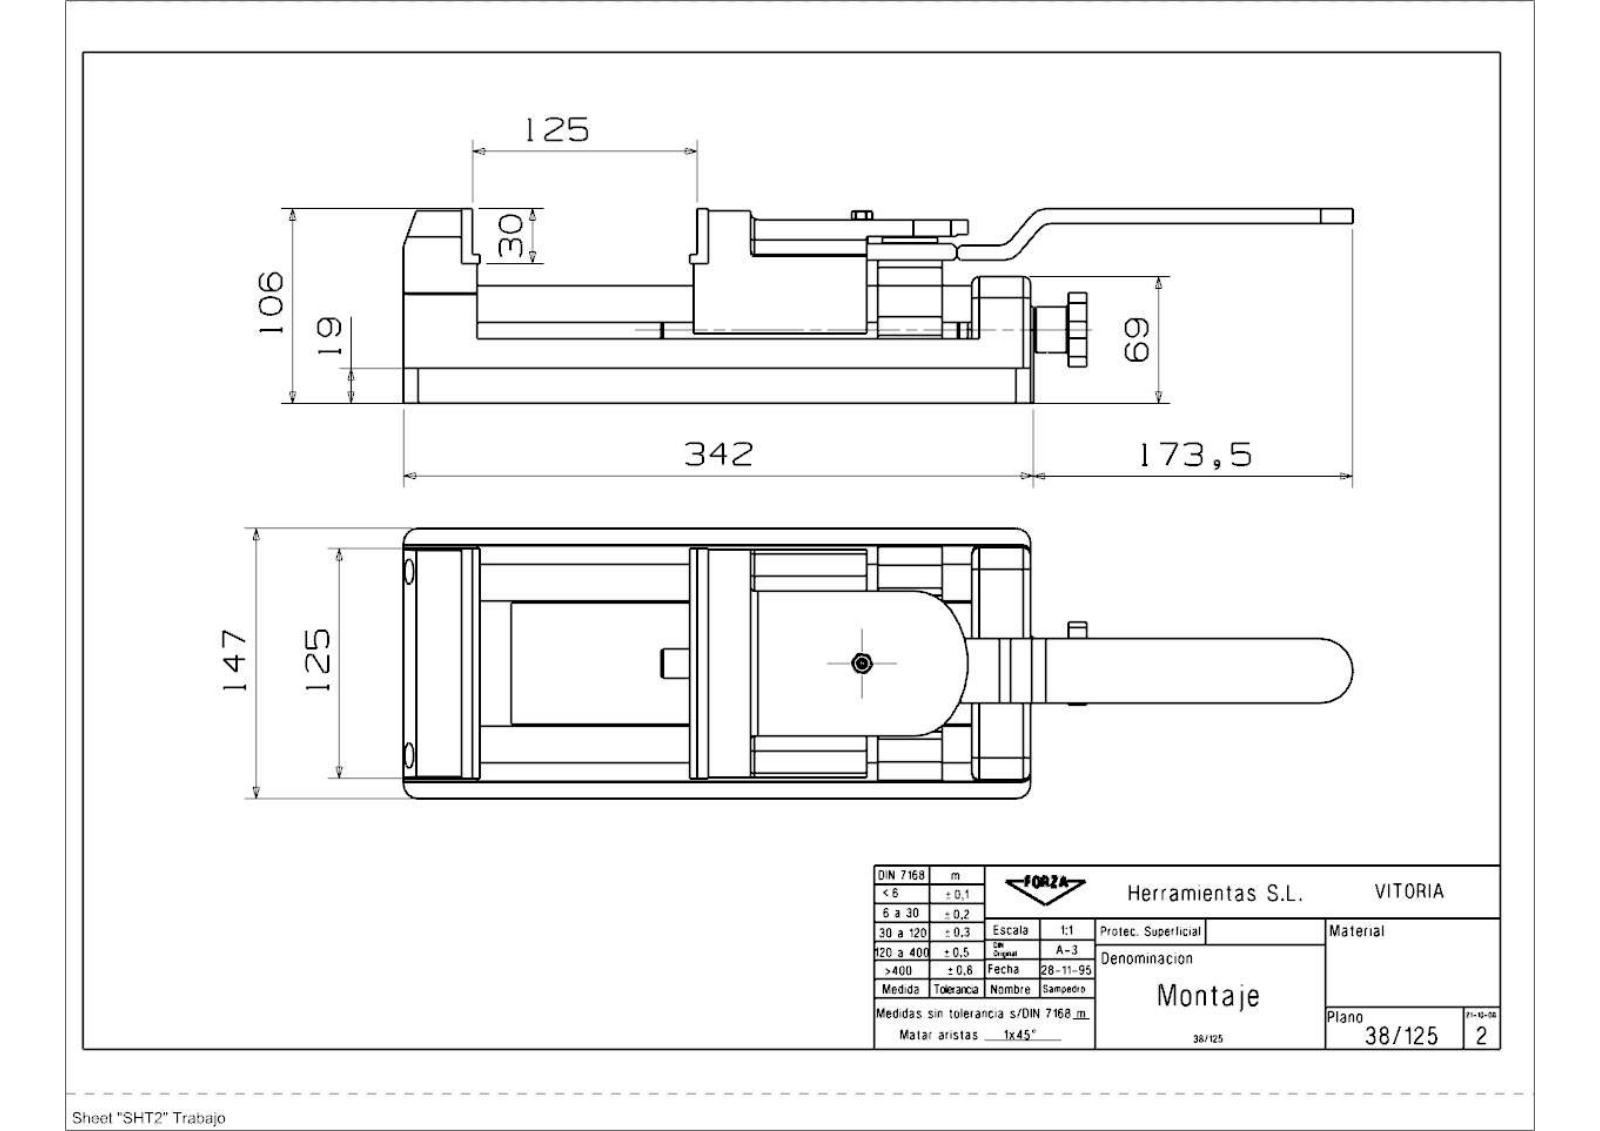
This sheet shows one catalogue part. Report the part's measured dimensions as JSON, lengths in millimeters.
{"part_name": "38_125_Mordaza", "step_written_by": "SIEMENS PLM Software NX 7.5 (AUTOMOTIVE_DESIGN)", "units": "millimeters", "bodies": {"solids": 15, "faces": 391, "planar": 177, "cylindrical": 144, "other": 70}, "overall_size": [518.5, 147, 106], "volume_mm3": 2399000, "surface_area_mm2": 382564, "round_holes": [[6.99, 3], [8.78, 3], [20, 3], [8.4, 2], [14, 2], [3, 1], [5, 1], [6, 1], [8, 1], [12, 1], [12.1, 1], [14.19, 1]], "round_bosses_or_shafts": [[68, 1], [42, 1], [30, 1], [25, 1], [19.9, 1], [16, 1], [11.6, 1], [9.73, 1]], "partial_cylinders_radius": [[4, 14], [10, 14], [8, 9], [7, 8], [12, 8], [5, 6], [3, 4], [2, 3]], "face_to_face_distances": [35, 29, 6, 95, 3, 32, 2, 19, 8, 16], "hole_center_spacings": [40.45, 46.17, 51.42, 52.15, 73.59, 102.16, 4.72, 23.84]}
